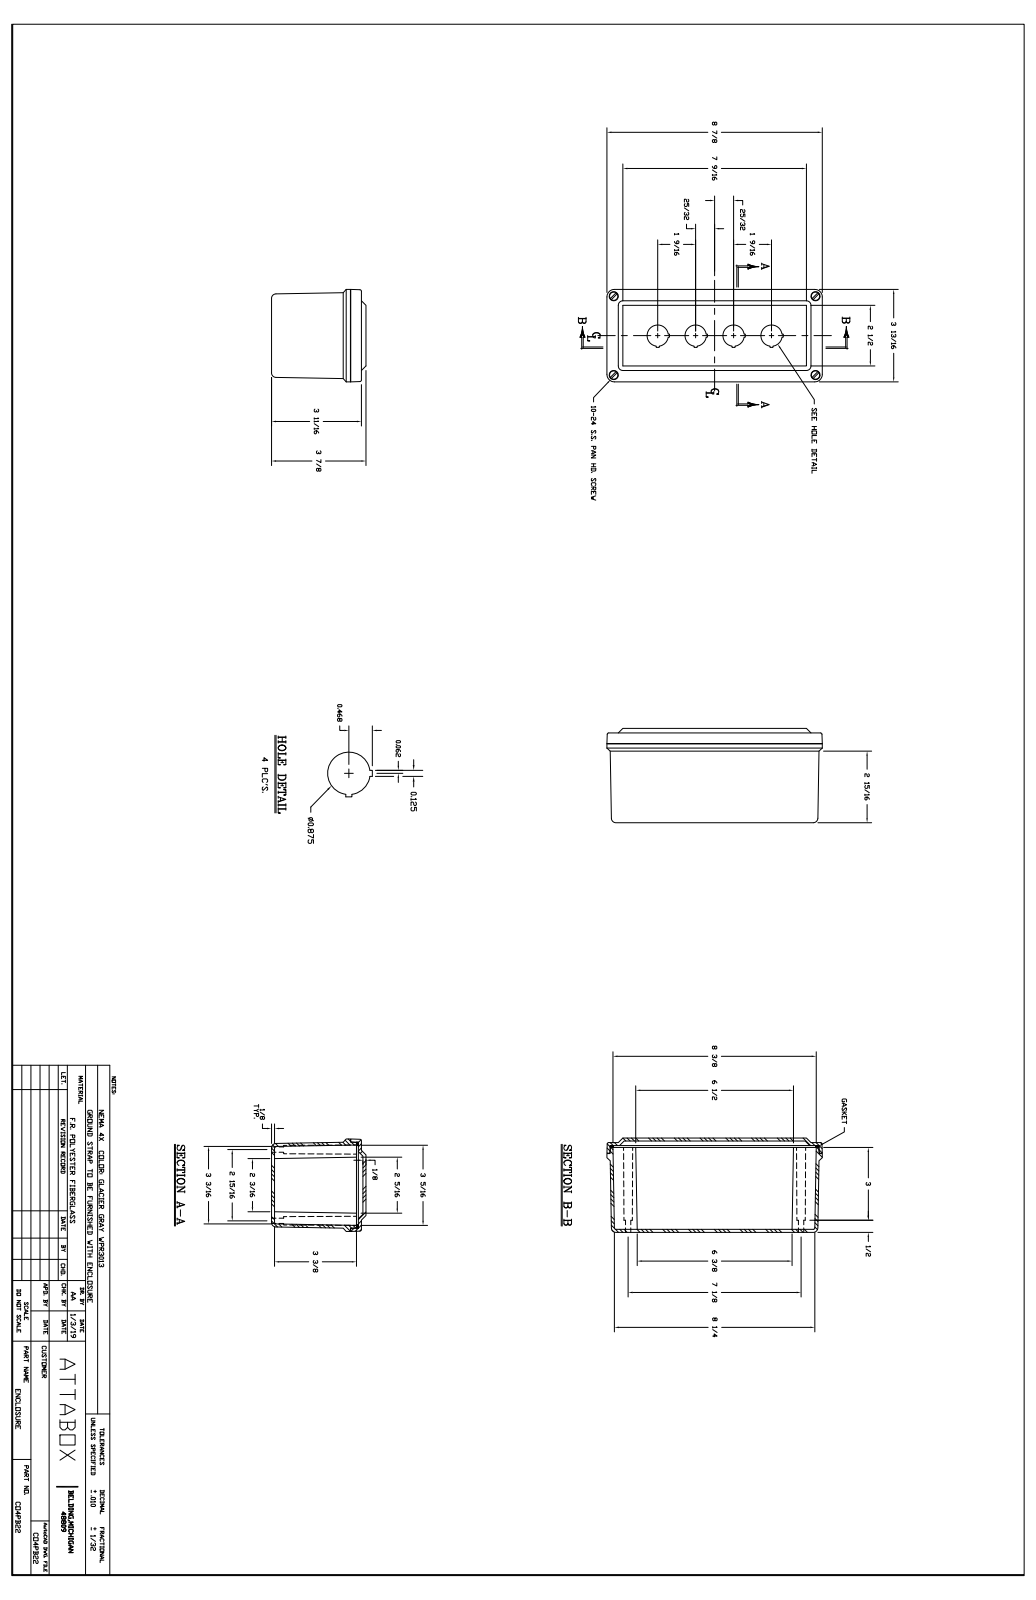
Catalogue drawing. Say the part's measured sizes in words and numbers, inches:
The part is named "CO4PB22". Its 3-D file was written by "SolidWorks 2018 (AUTOMOTIVE_DESIGN)". It is 1 solid with 410 faces: 206 planar, 112 cylindrical and 92 other. Overall it measures 8.875 by 3.875 by 3.813 inches. Its volume is 24.63 cubic inches and its surface area 312.9 square inches. Round holes: 8 of diameter 0.219, 4 of diameter 0.19, 4 of diameter 0.375, 2 of diameter 0.875, 2 of diameter 0.875. Round bosses or shafts: 4 of diameter 0.371, 4 of diameter 0.218, 4 of diameter 0.177. Partial cylindrical surfaces (rounded edges, fillets, slot ends): 20 of radius 0.031, 16 of radius 0.012, 4 of radius 0.176, 4 of radius 0.188, 4 of radius 0.22, 4 of radius 0.313, 4 of radius 0.325, 2 of radius 0.062. The main face-to-face distances are 0.125, 0.135, 3.75, 3.875, 3.625, 0.187, 3.563, 0.134, 0.063, 0.5. The hole center spacings are 0.576, 1.909, 2.39, 3.114, 3.146, 3.704, 4.585, 5.159.
